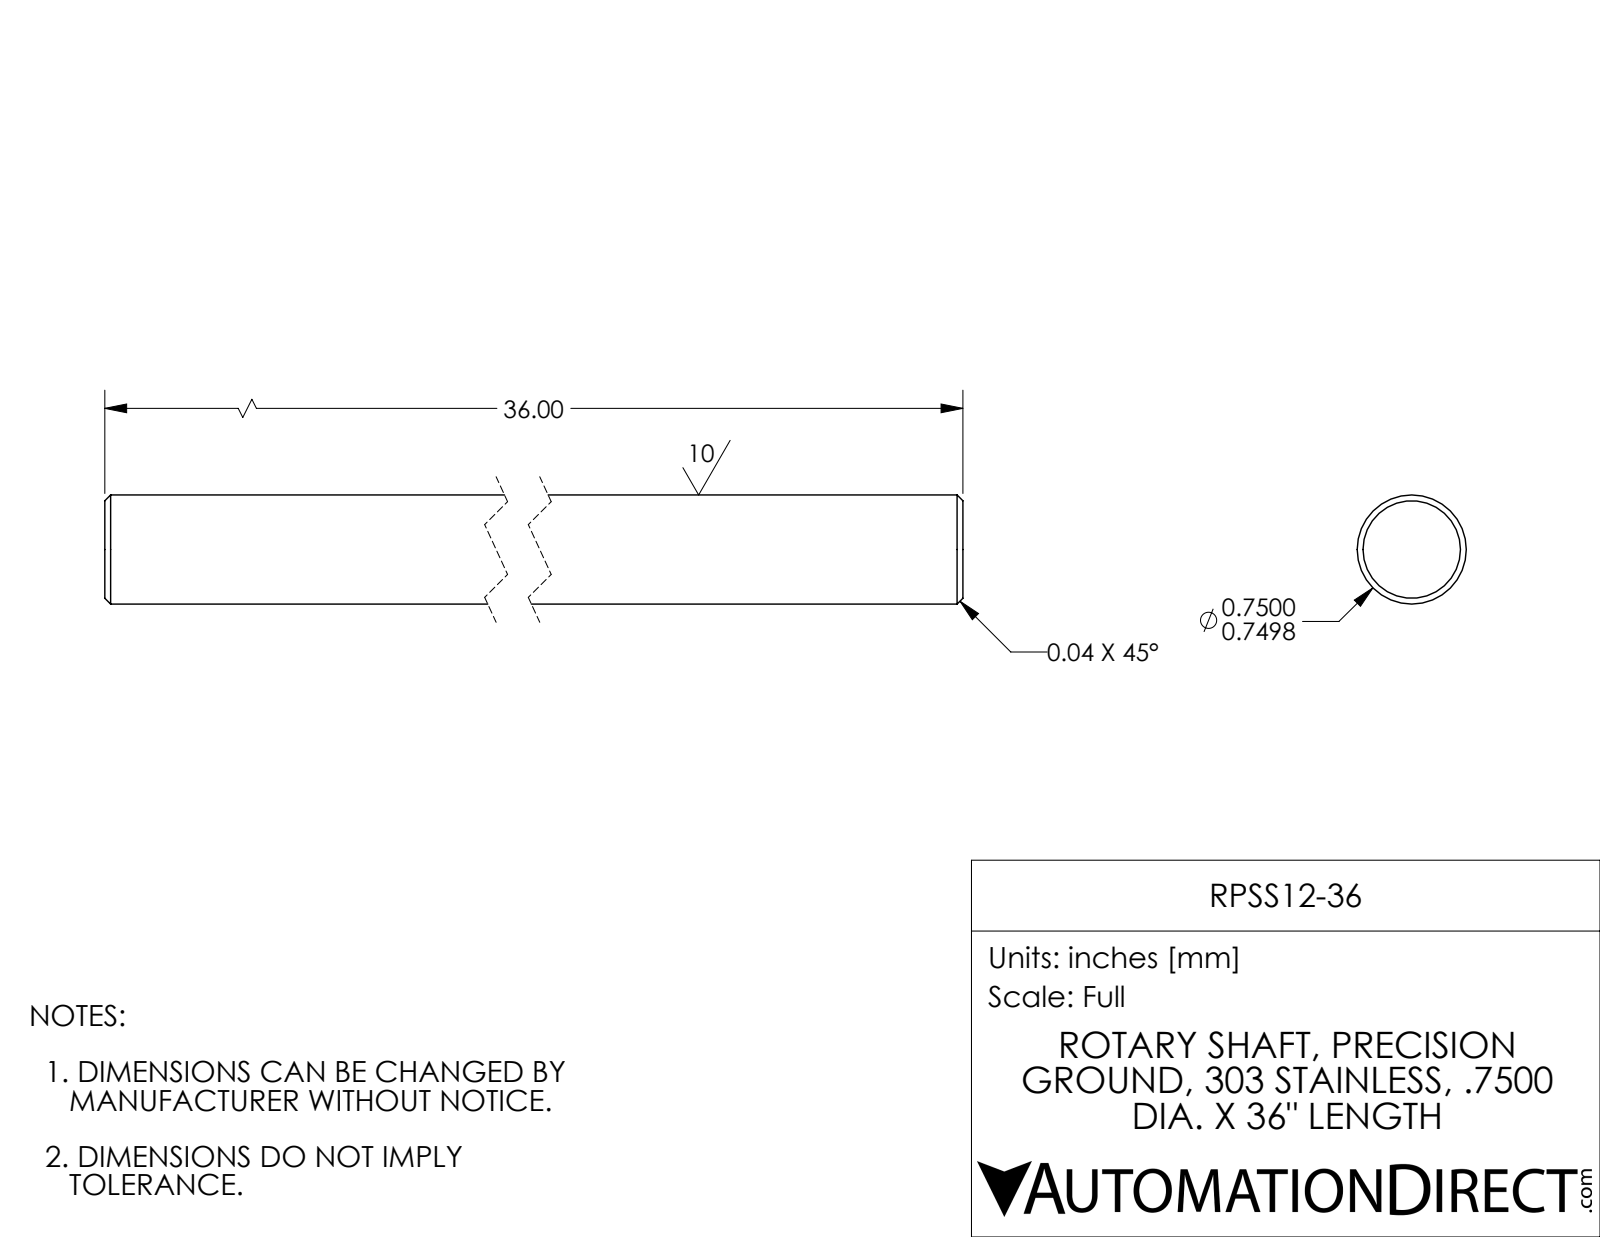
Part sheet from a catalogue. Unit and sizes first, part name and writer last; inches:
Units: inches
Overall size (bounding box): 36 × 0.75 × 0.75
Round bosses / shafts (diameter × count): ⌀0.75 ×1
Main face-to-face distances: 36
Volume: 15.9 in³ · Surface area: 85.59 in²
Bodies: 1 solid, 8 faces (2 planar, 2 cylindrical, 4 other)
Part name (STEP PRODUCT): RPSS12-36
STEP written by: SolidWorks 2017 (AUTOMOTIVE_DESIGN)
